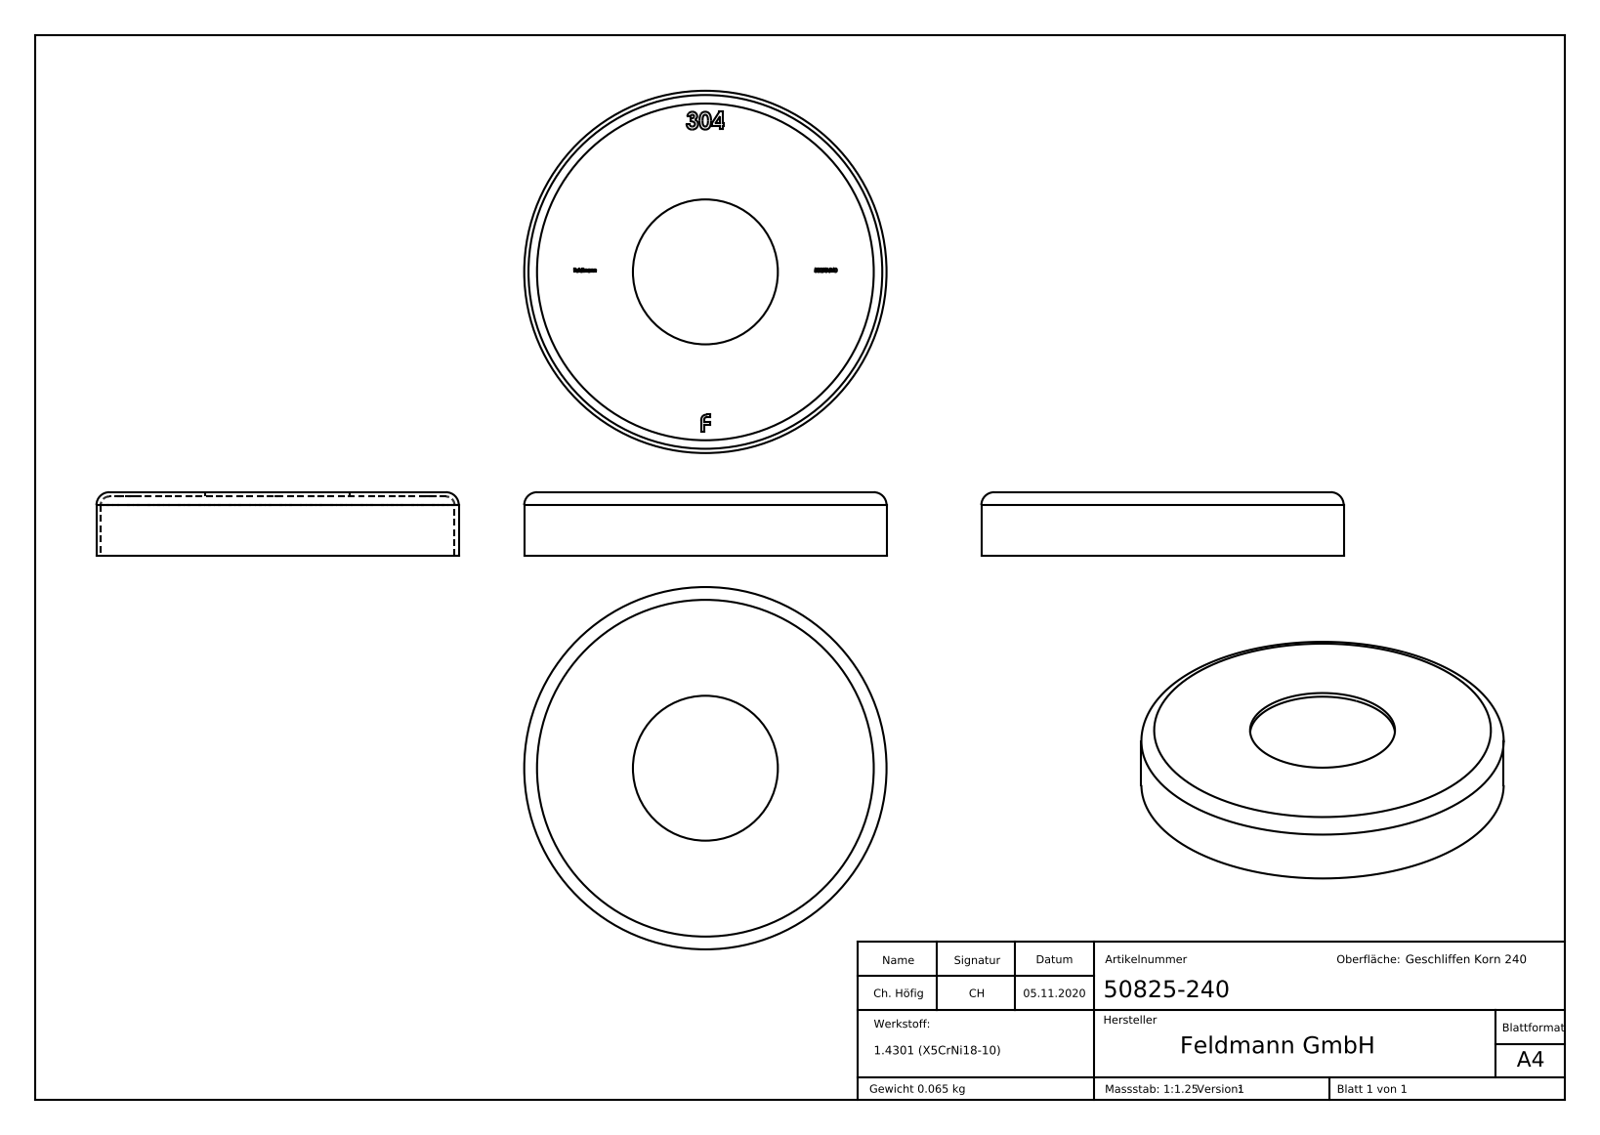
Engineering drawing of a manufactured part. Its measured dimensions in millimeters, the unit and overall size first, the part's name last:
Units: millimetres
Overall size (bounding box): 85 × 85 × 15
Round holes (diameter × count): ⌀34 ×1, ⌀83 ×1
Round bosses / shafts (diameter × count): ⌀85 ×1
Main face-to-face distances: 1, 14, 15, 14.1, 0.9, 0.71, 5, 4.29, 0.58, 0.69
Volume: 8 172 mm³ · Surface area: 16 735 mm²
Bodies: 1 solid, 302 faces (156 planar, 6 cylindrical, 140 other)
Part name (STEP PRODUCT): 50825-240
STEP written by: SolidWorks 2018 (CONFIG_CONTROL_DESIGN)
